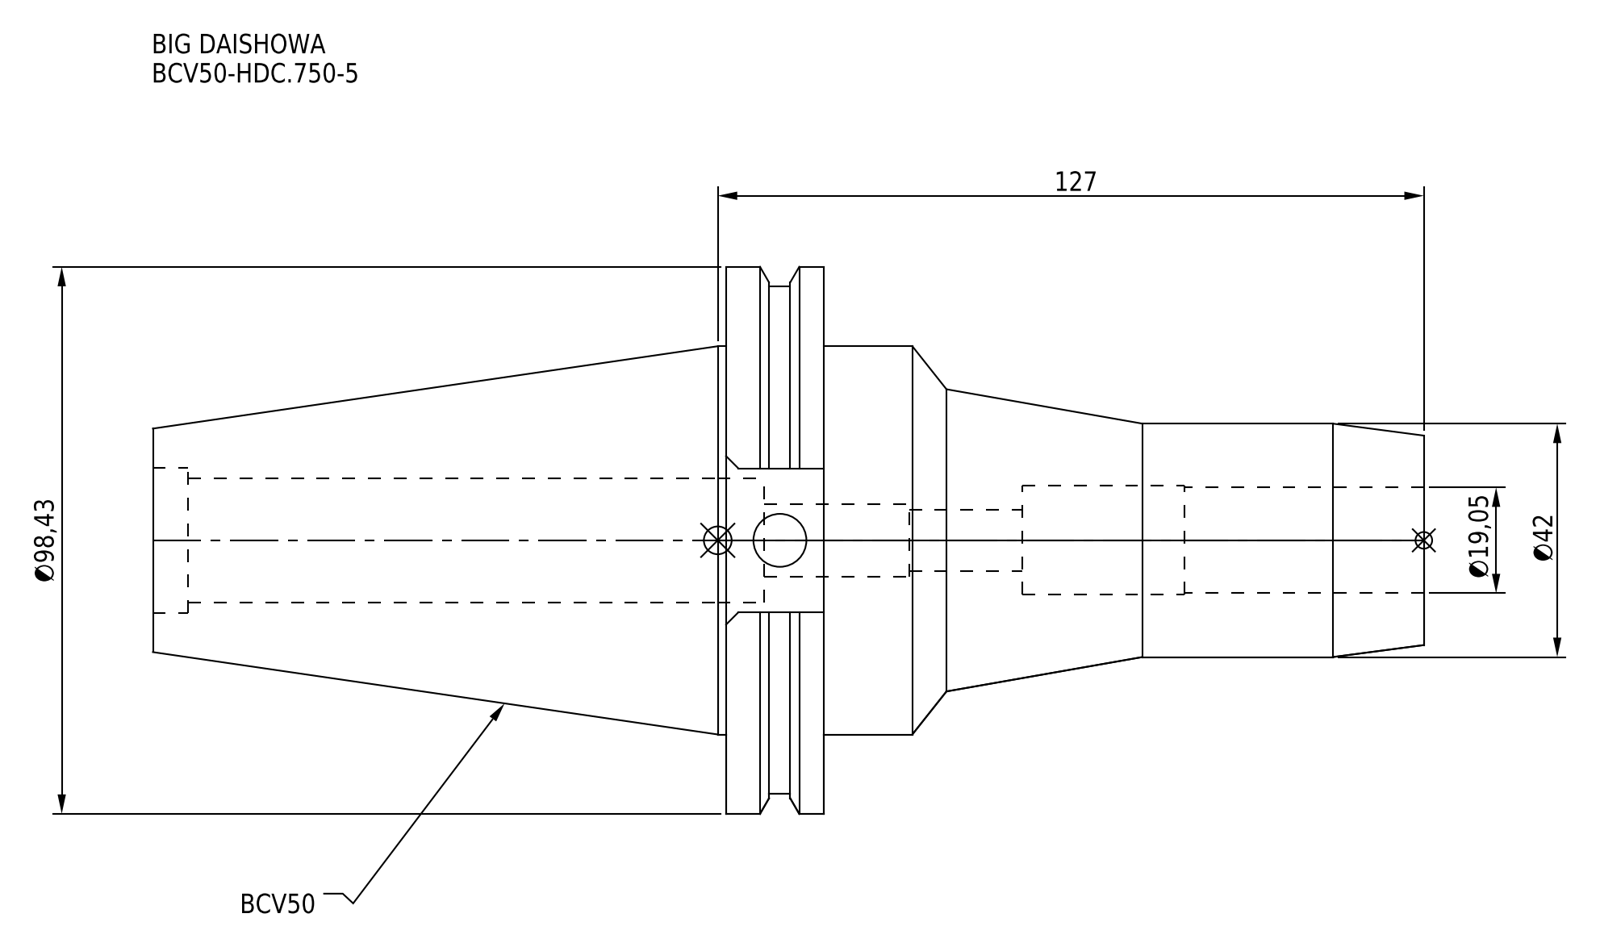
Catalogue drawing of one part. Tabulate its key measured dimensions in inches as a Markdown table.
| quantity | value |
| --- | --- |
| part name | BCV50-HDC_750-5 |
| STEP written by | CREO PARAMETRIC BY PTC INC, 2016380 (AUTOMOTIVE_DESIGN) |
| units | inches |
| bodies | 1 solid, 64 faces (24 planar, 28 cylindrical, 12 other) |
| overall size | 9 × 3.875 × 3.738 |
| volume | 31.31 in³ |
| surface area | 100.9 in² |
| round holes (diameter × count) | 0.375 × 1, 0.433 × 1, 0.512 × 1, 0.75 × 1, 0.772 × 1, 0.878 × 1, 1.033 × 1 |
| round bosses / shafts (diameter × count) | 3.875 × 1, 3.594 × 1, 2.75 × 1, 1.654 × 1 |
| main face-to-face distances | 0.691, 4.25, 4.941, 9, 4.75, 4.059, 2.872, 1.02, 4.669, 0.419 |
